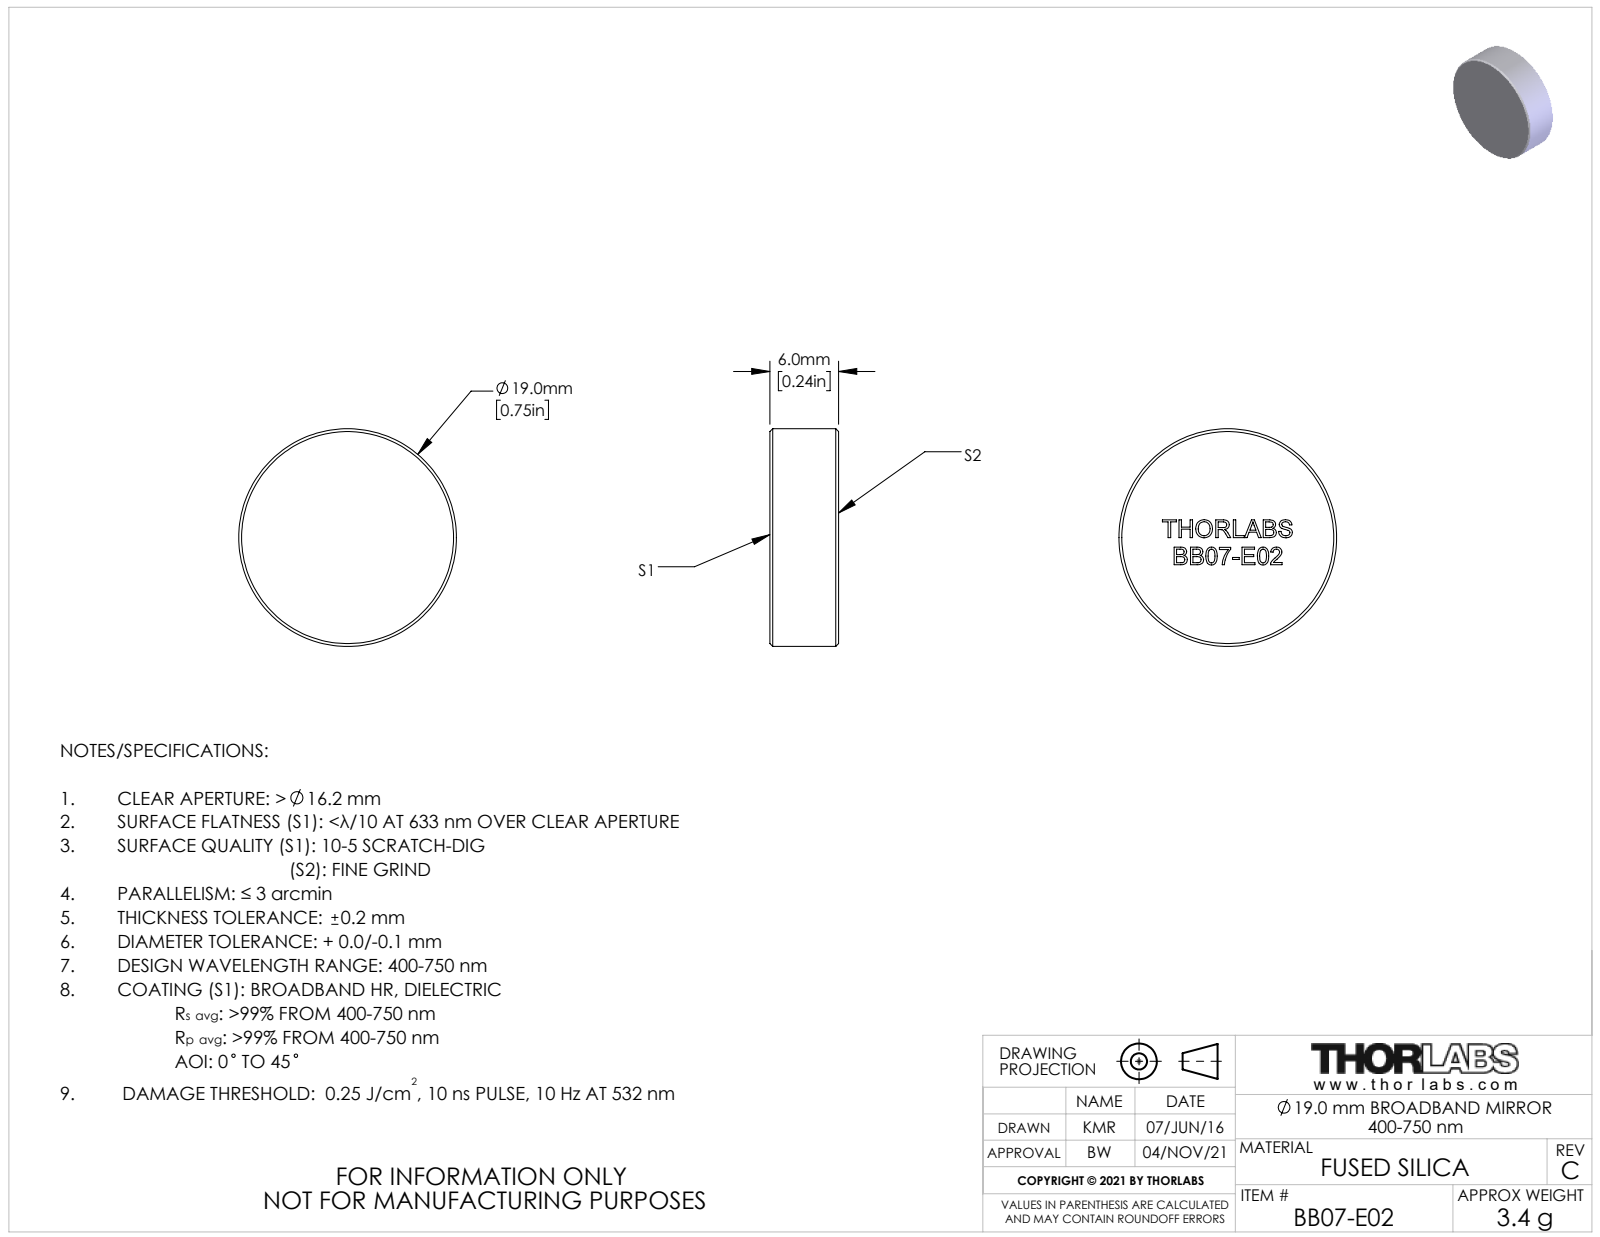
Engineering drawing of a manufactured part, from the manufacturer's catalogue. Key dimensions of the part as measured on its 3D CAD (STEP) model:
Part name (STEP PRODUCT): TTN024106-E0W
STEP written by: SolidWorks 2016 (CONFIG_CONTROL_DESIGN)
Units: millimetres
Bodies: 1 solid, 231 faces (131 planar, 2 cylindrical, 98 other)
Overall size (bounding box): 19 × 19 × 6
Volume: 1 697 mm³ · Surface area: 908 mm²
Round bosses / shafts (diameter × count): ⌀19 ×1
Main face-to-face distances: 6, 1.54, 2.37, 1.36, 4.15, 1.92, 2.39, 3.2, 0.53, 0.83
